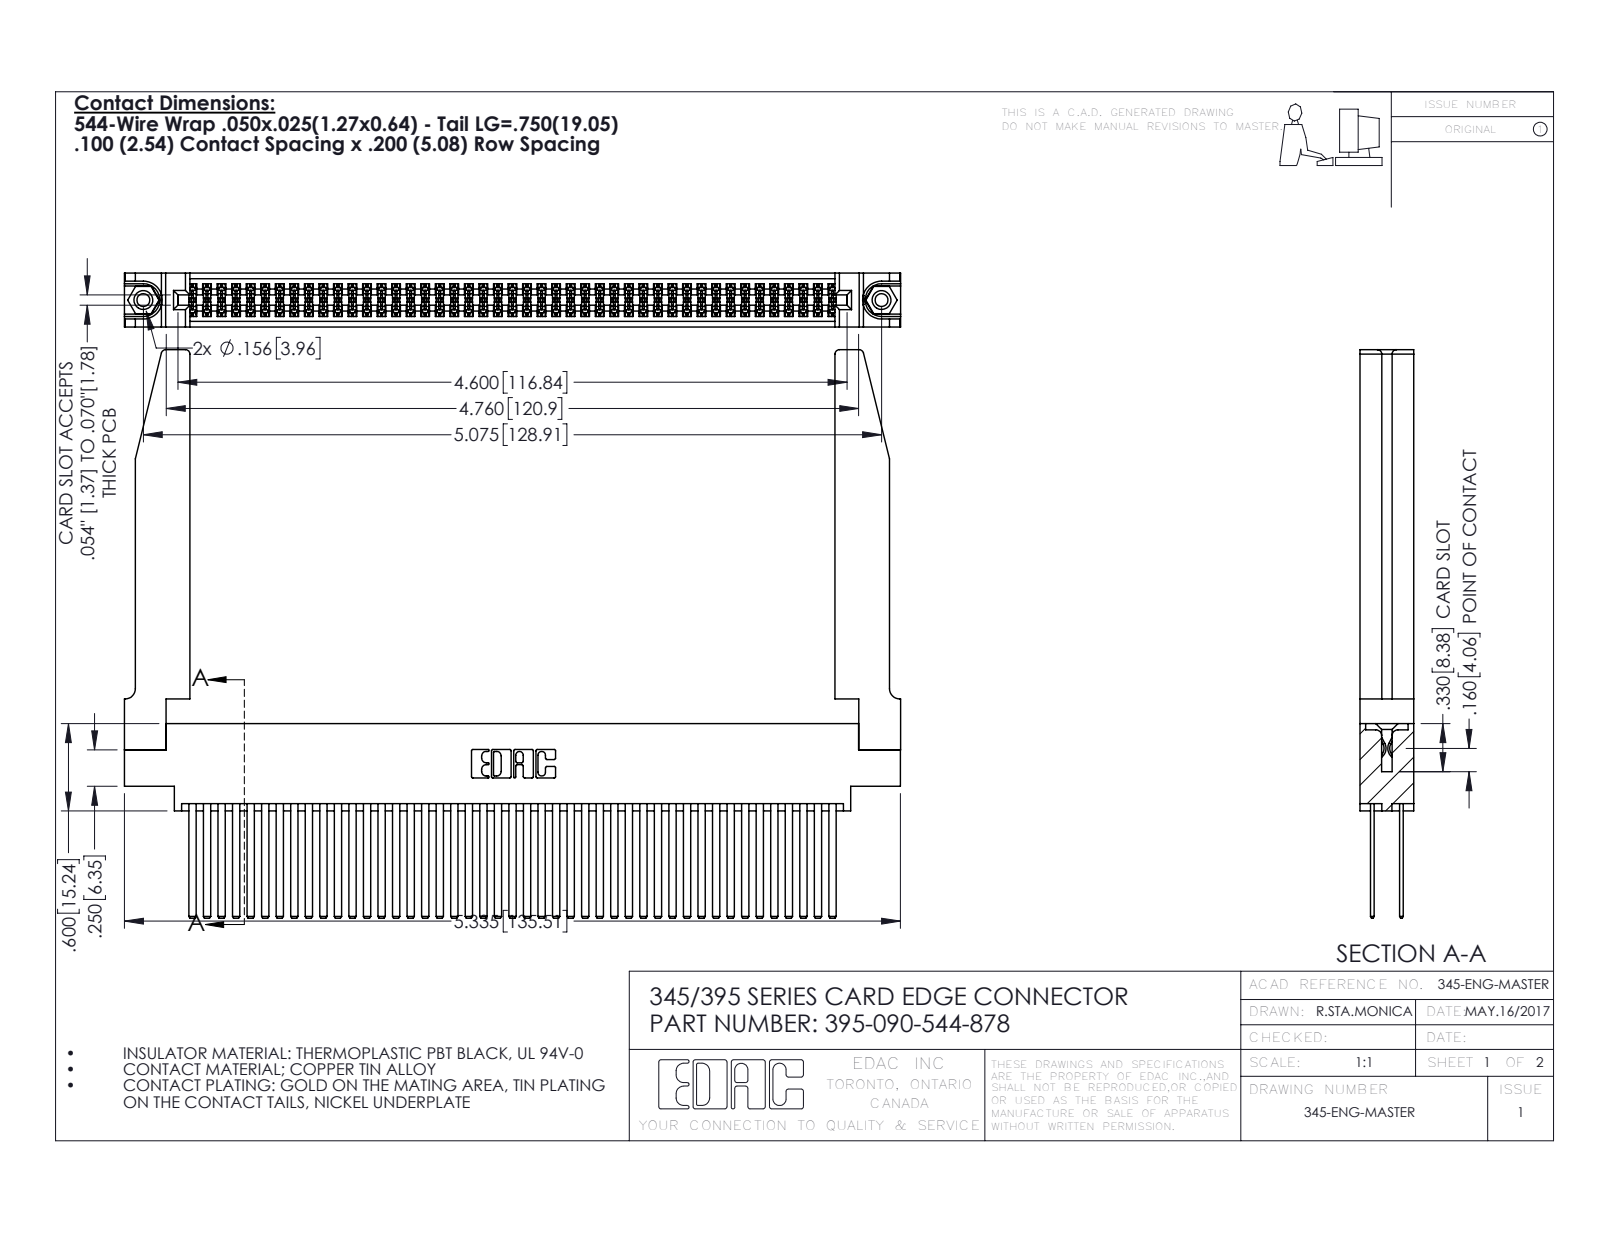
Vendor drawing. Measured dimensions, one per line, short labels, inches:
name: 395-090-544-878; 345-220-078_345-220-078; 345 Part_0.170 Offset - 0.156 Dia-TH; 345-250-001_345-250-001-102 (+1 more)
written by: SolidWorks 2016 (CONFIG_CONTROL_DESIGN)
unit: in
bodies: 95 solids, 4324 faces (2836 planar, 1436 cylindrical, 52 other)
size: 5.336 × 3.907 × 0.37
volume: 1.349 in³; area: 49.5 in²
holes: 2× ⌀0.089, 2× ⌀0.125, 2× ⌀0.156, 1× ⌀0.064
bosses: 2× ⌀0.155
rounds: 135× R0.006, 22× R0.01, 8× R0.03, 6× R0.007, 6× R0.031, 3× R0.026, 2× R0.014, 2× R0.019
face distances: 0.072, 0.298, 0.098, 0.272, 0.025, 0.2, 0.37, 0.225, 0.175, 0.148
hole spacings: 0.27, 4.839, 5.075
